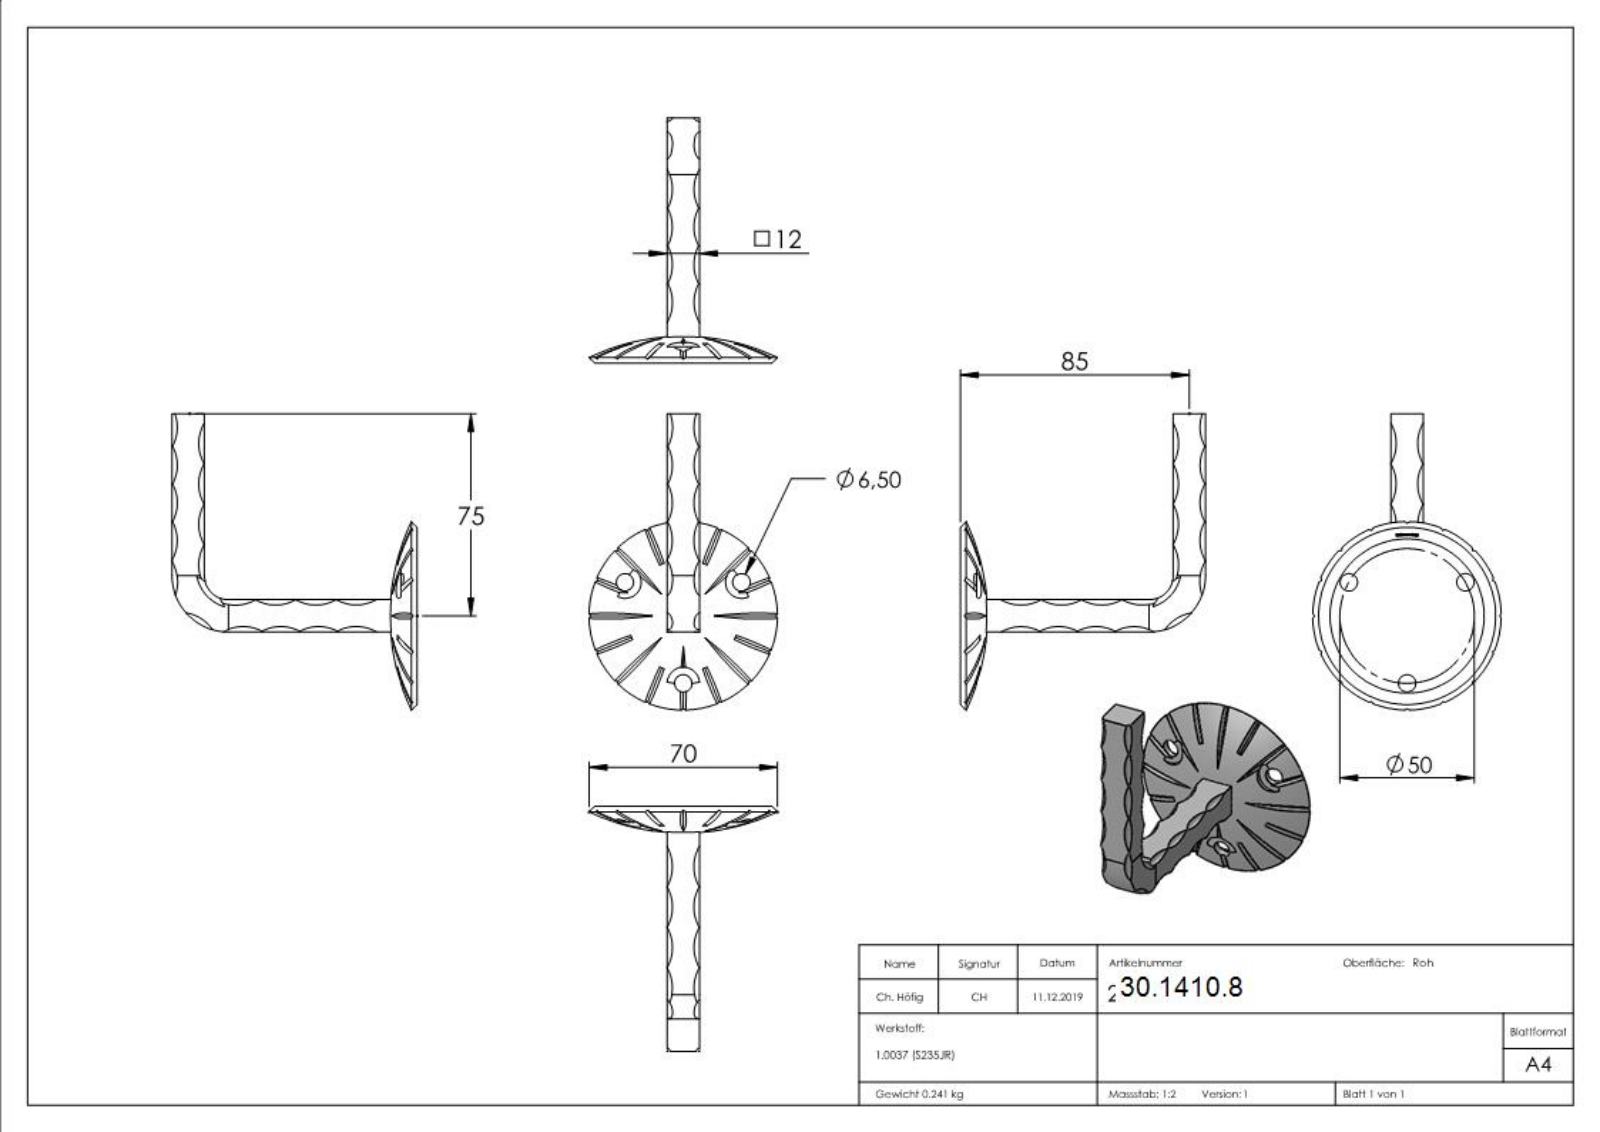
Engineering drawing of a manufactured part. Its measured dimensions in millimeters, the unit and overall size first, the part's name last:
Units: millimetres
Overall size (bounding box): 109.99 × 91 × 69.98
Round holes (diameter × count): ⌀6.5 ×3
Partial cylindrical surfaces — rounded edges, fillets, slot ends (radius × count): R6 ×3, R9 ×1, R21 ×1
Main face-to-face distances: 12, 79, 91, 81, 69, 85, 73, 6, 90.5, 78.5
Hole centre spacings: 43.3
Volume: 30 833 mm³ · Surface area: 15 494 mm²
Bodies: 1 solid, 280 faces (109 planar, 12 cylindrical, 159 other)
Part name (STEP PRODUCT): 2502
STEP written by: SolidWorks 2015 (CONFIG_CONTROL_DESIGN)
